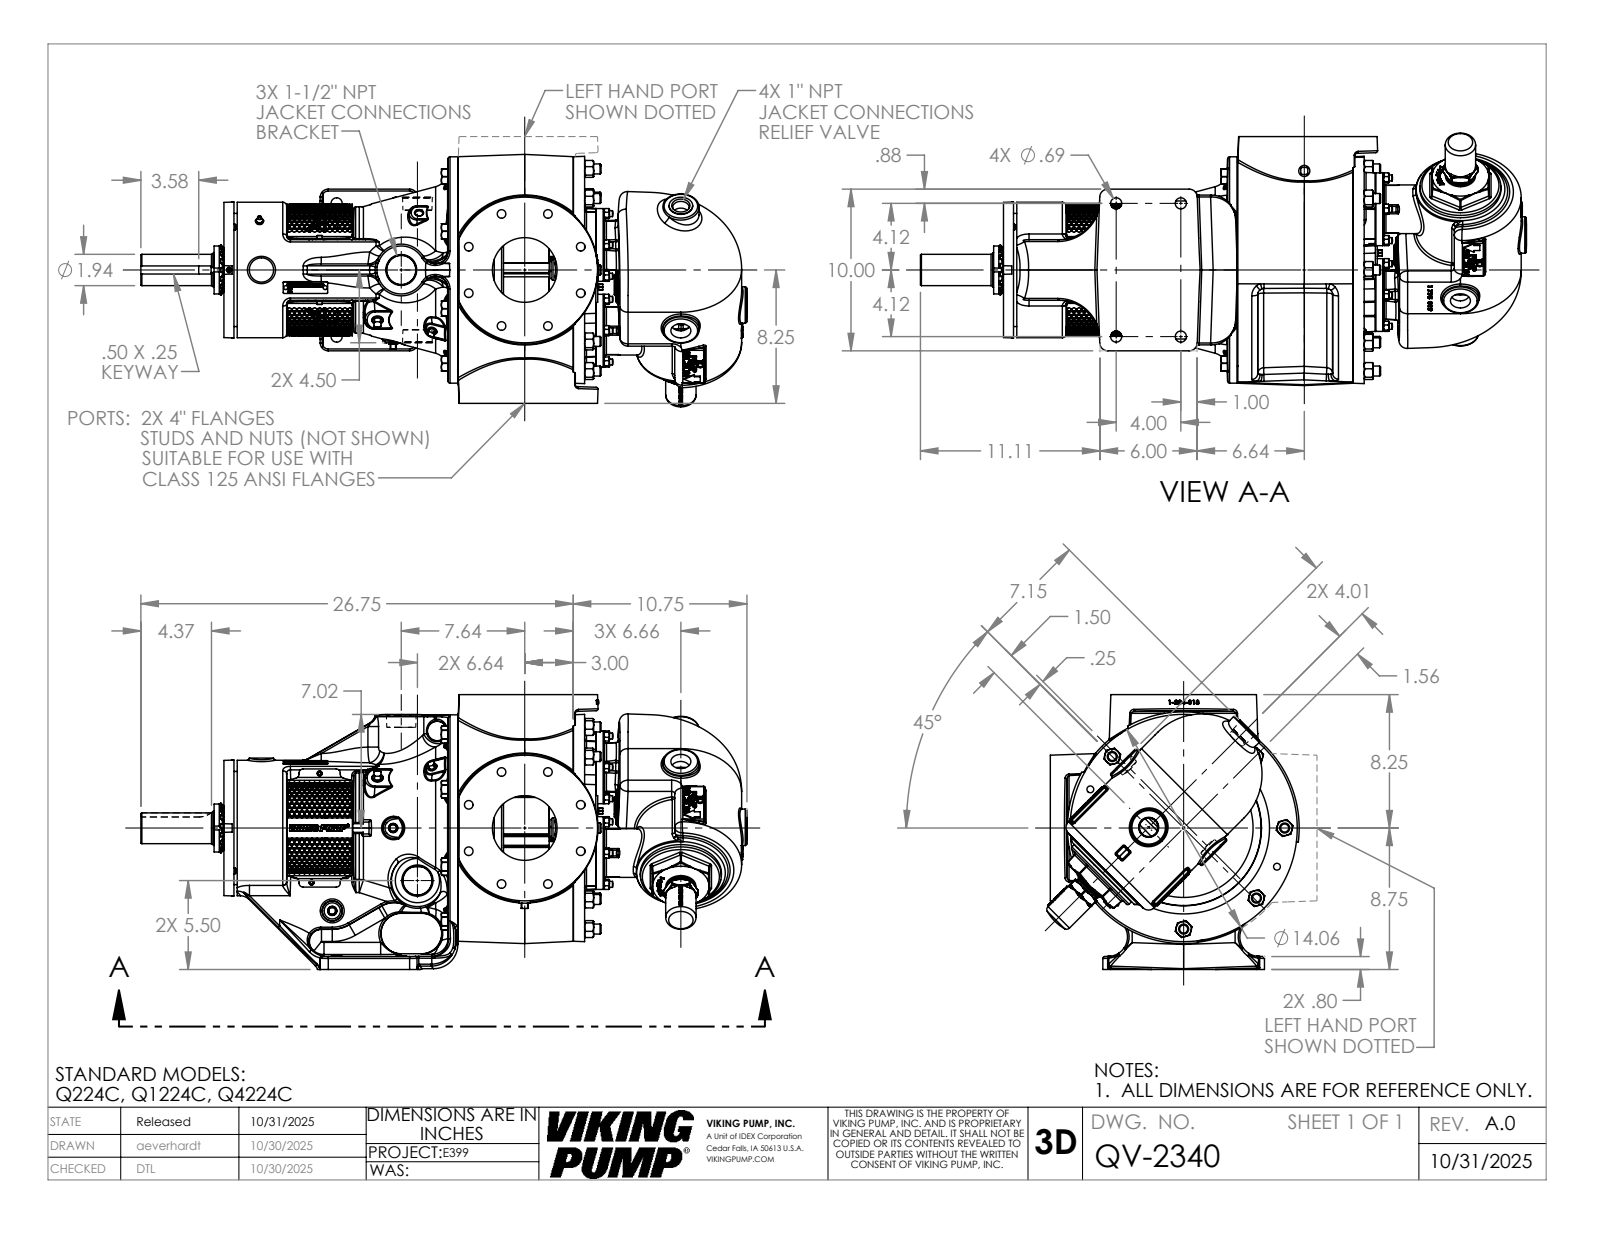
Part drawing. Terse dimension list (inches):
name: QV-2340
written by: SolidWorks 2024 (AUTOMOTIVE_DESIGN)
unit: in
bodies: 1 solid, 5063 faces (1637 planar, 725 cylindrical, 2701 other)
size: 37.499 × 19.211 × 17.61
volume: 2 837 in³; area: 2 495 in²
holes: 8× ⌀0.266, 8× ⌀1.157, 6× ⌀0.25, 4× ⌀0.531, 4× ⌀0.688, 2× ⌀0.159, 2× ⌀0.313, 2× ⌀0.422, 1× ⌀0.453, 1× ⌀1, 1× ⌀2.157, 1× ⌀2.167
bosses: 24× ⌀0.617, 14× ⌀0.625, 8× ⌀0.369, 3× ⌀0.437, 3× ⌀0.312, 2× ⌀4.5, 2× ⌀0.625, 2× ⌀0.375
rounds: 62× R0.12, 28× R0.5, 26× R0.06, 22× R0.75, 18× R0.015, 18× R0.092, 16× R0.07, 16× R0.19
face distances: 17, 22.317, 1.25, 3.82, 18.498, 7.972, 4.153, 14.345, 1.5, 20.817
hole spacings: 3.75, 2.079, 5.783, 2.713, 3.133, 3.788, 5.423, 5.932
